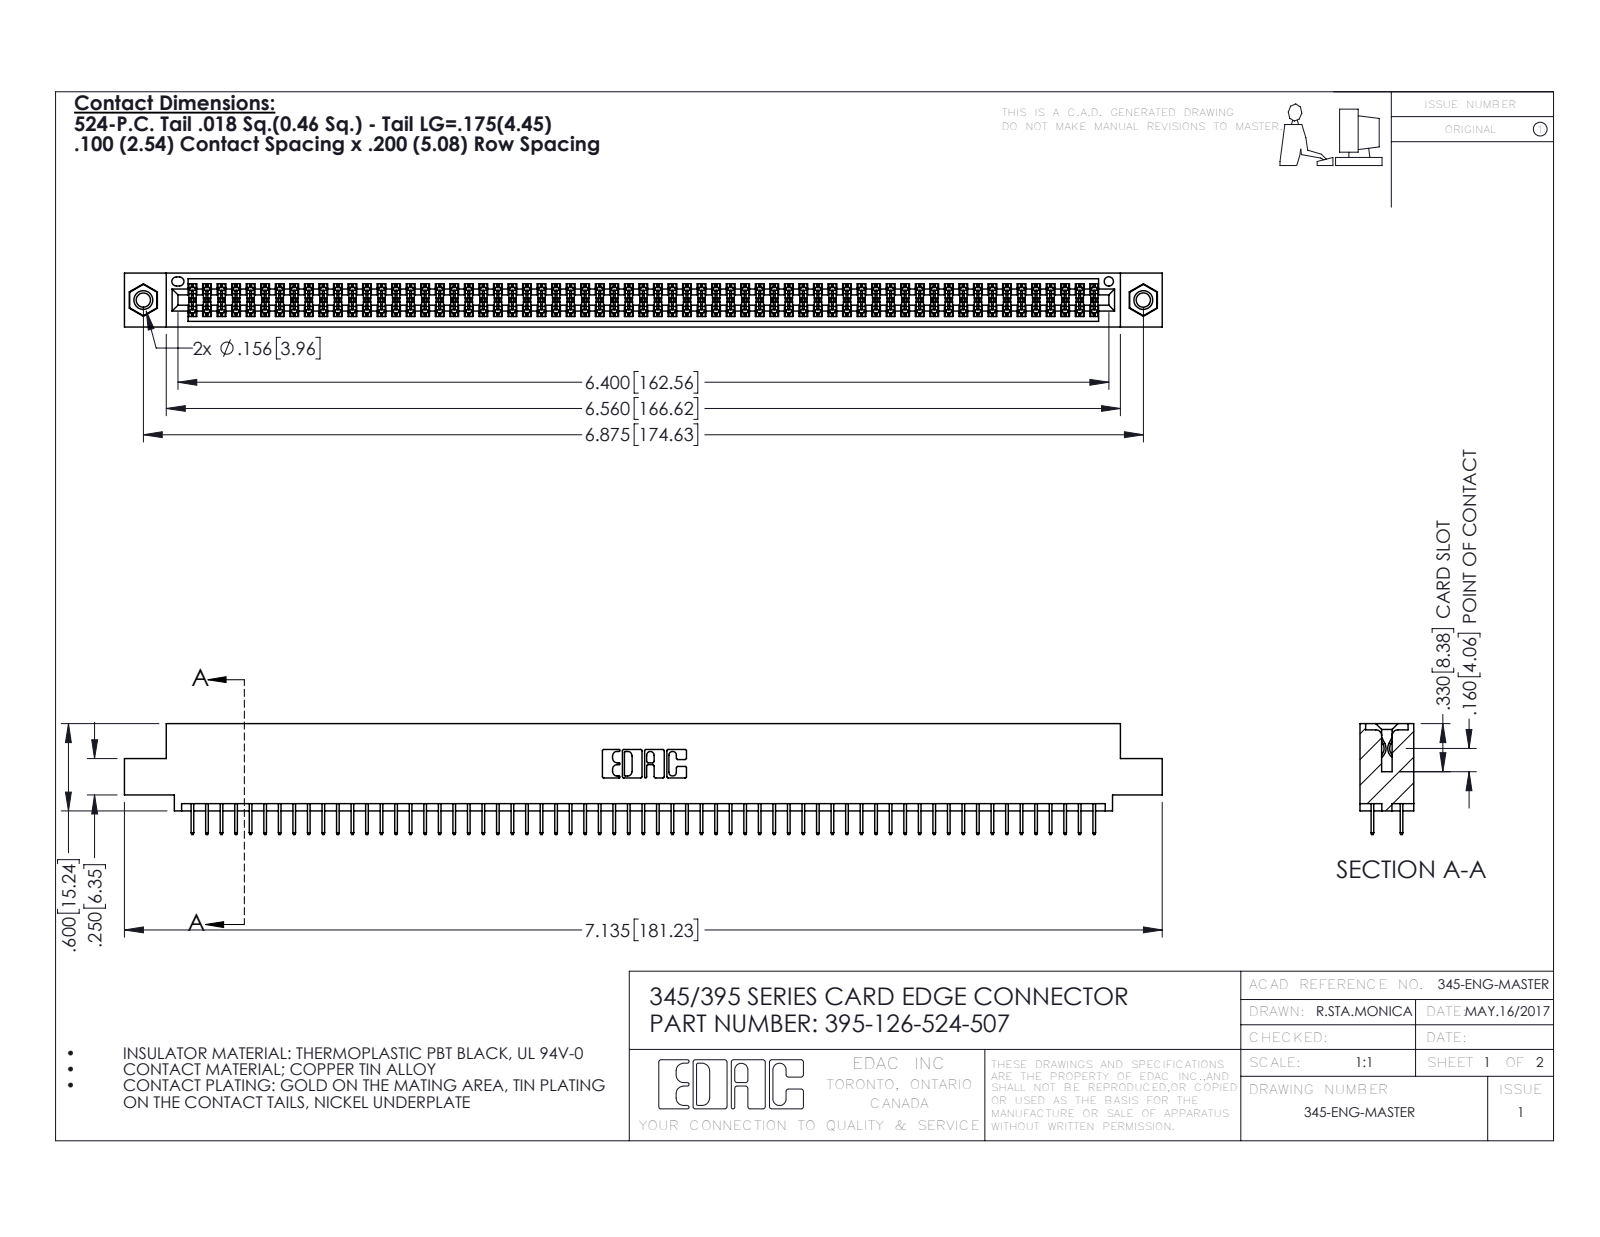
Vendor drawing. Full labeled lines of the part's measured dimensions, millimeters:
Part name (STEP PRODUCT): 345-292-001_345-293-124; 345-250-001_345-250-005-103; 395-126-524-507; 345 Part_0.110 Offset - 0.156 Dia-TI
STEP written by: SolidWorks 2016 (CONFIG_CONTROL_DESIGN)
Units: millimetres
Bodies: 129 solids, 6994 faces (5030 planar, 1948 cylindrical, 16 other)
Overall size (bounding box): 181.2 × 19.4 × 9.4
Volume: 17 520 mm³ · Surface area: 25 920 mm²
Round holes (diameter × count): ⌀2.5 ×2, ⌀3.2 ×2, ⌀4 ×2, ⌀1.6 ×1
Round bosses / shafts (diameter × count): ⌀3.9 ×2
Partial cylindrical surfaces — rounded edges, fillets, slot ends (radius × count): R0.2 ×189, R0.3 ×22, R0.2 ×6, R0.8 ×6, R0.7 ×3, R0.4 ×2, R0.5 ×2, R0.6 ×2
Main face-to-face distances: 1.8, 7.6, 5.1, 9.4, 2.5, 6.9, 0.6, 5.7, 1.8, 4.4
Hole centre spacings: 6.9, 168.6, 174.6
